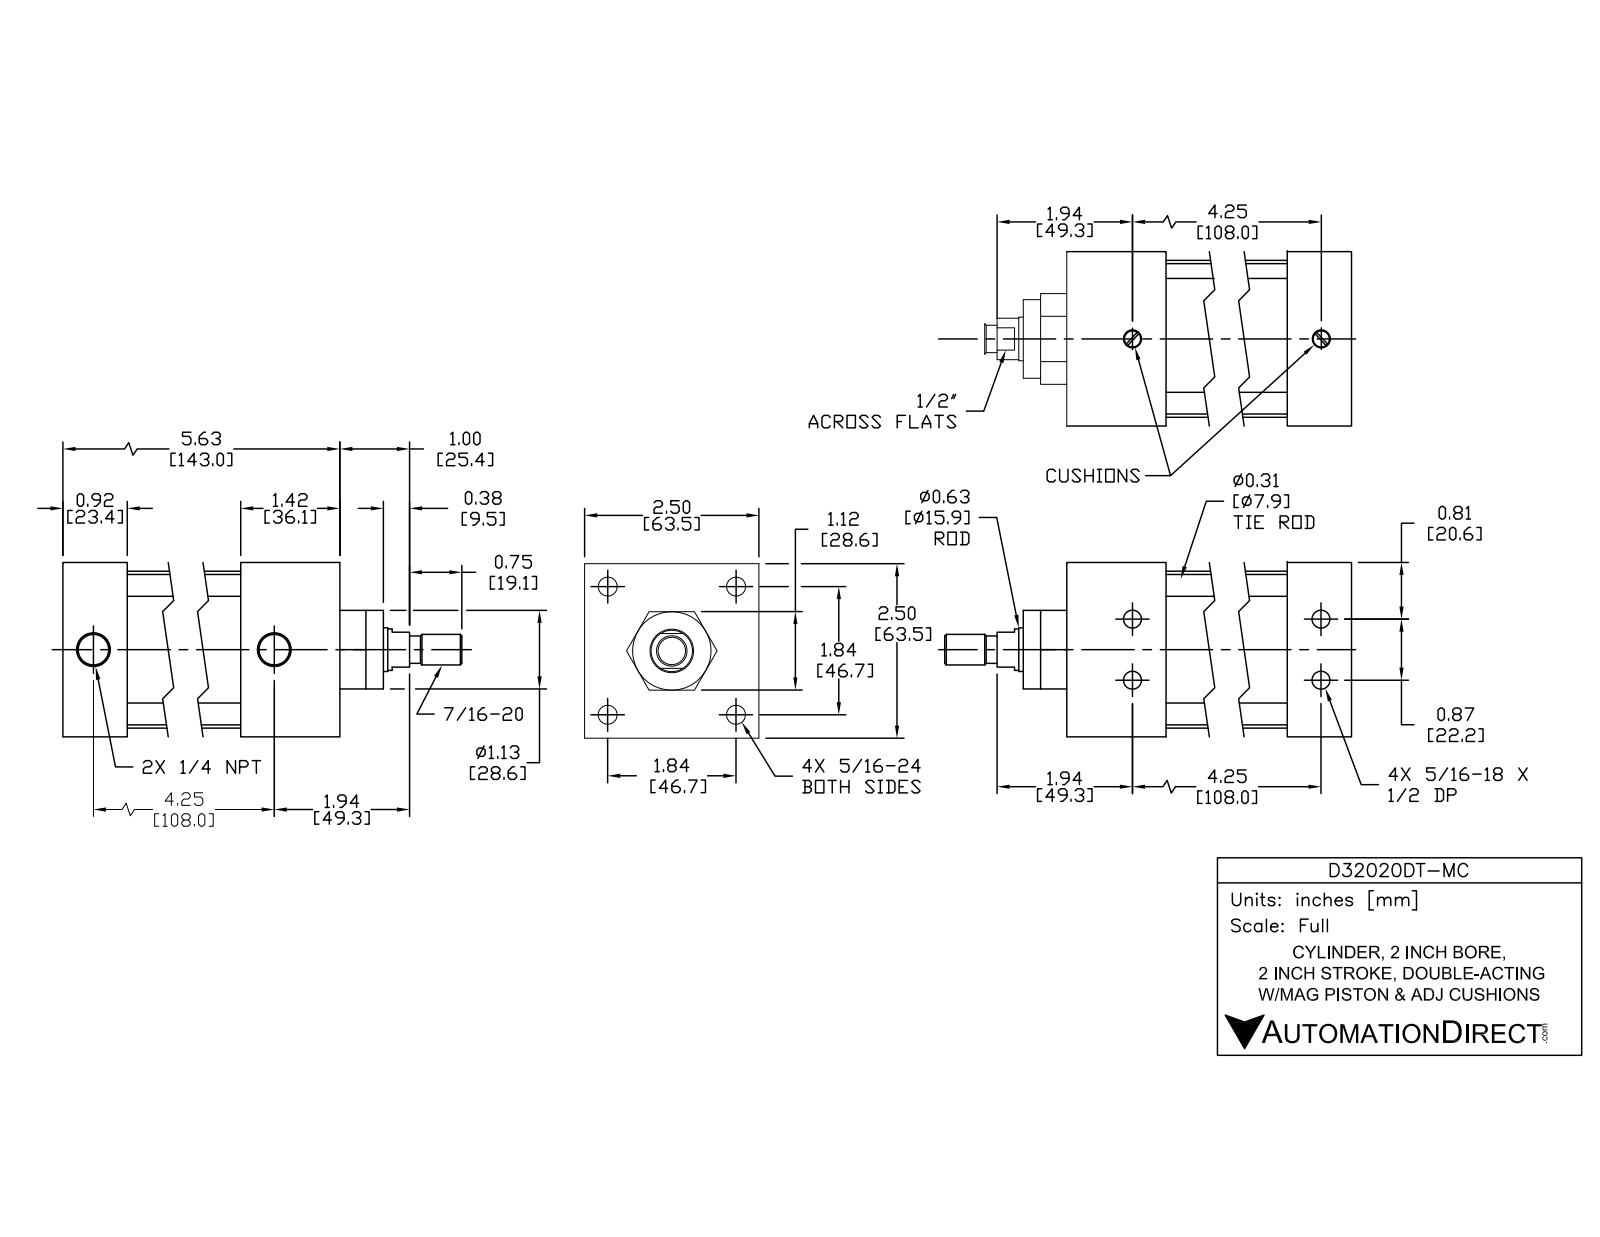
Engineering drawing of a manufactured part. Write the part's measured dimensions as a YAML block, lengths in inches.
part_name: "D32020DT-M BODY; D32020DT-MC; D32020DT-M PISTON"
step_written_by: "SolidWorks 2015 (AUTOMOTIVE_DESIGN)"
units: inches
bodies: {solids: 12, faces: 298, planar: 94, cylindrical: 114, other: 90}
overall_size: [7.371, 2.5, 2.5]
volume: 22.61
surface_area: 161.2
round_holes:
  - {diameter: 0.252, count: 4}
  - {diameter: 0.267, count: 4}
  - {diameter: 0.359, count: 4}
  - {diameter: 0.5, count: 4}
  - {diameter: 0.297, count: 2}
  - {diameter: 0.477, count: 2}
  - {diameter: 0.625, count: 1}
  - {diameter: 0.628, count: 1}
  - {diameter: 2, count: 1}
round_bosses_or_shafts:
  - {diameter: 0.484, count: 4}
  - {diameter: 0.313, count: 4}
  - {diameter: 0.282, count: 4}
  - {diameter: 2.25, count: 1}
  - {diameter: 1.997, count: 1}
  - {diameter: 1.12, count: 1}
  - {diameter: 0.622, count: 1}
  - {diameter: 0.59, count: 1}
partial_cylinders:
  - {radius: 0.25, count: 4}
face_to_face_distances: [2.5, 0.08, 3.201, 5.621, 1.42, 4.201, 3.281, 4.701, 0.92, 1]
hole_center_spacings: [4.267, 4.245, 0.437, 0.438, 0.875, 1.306, 1.307, 1.848]
